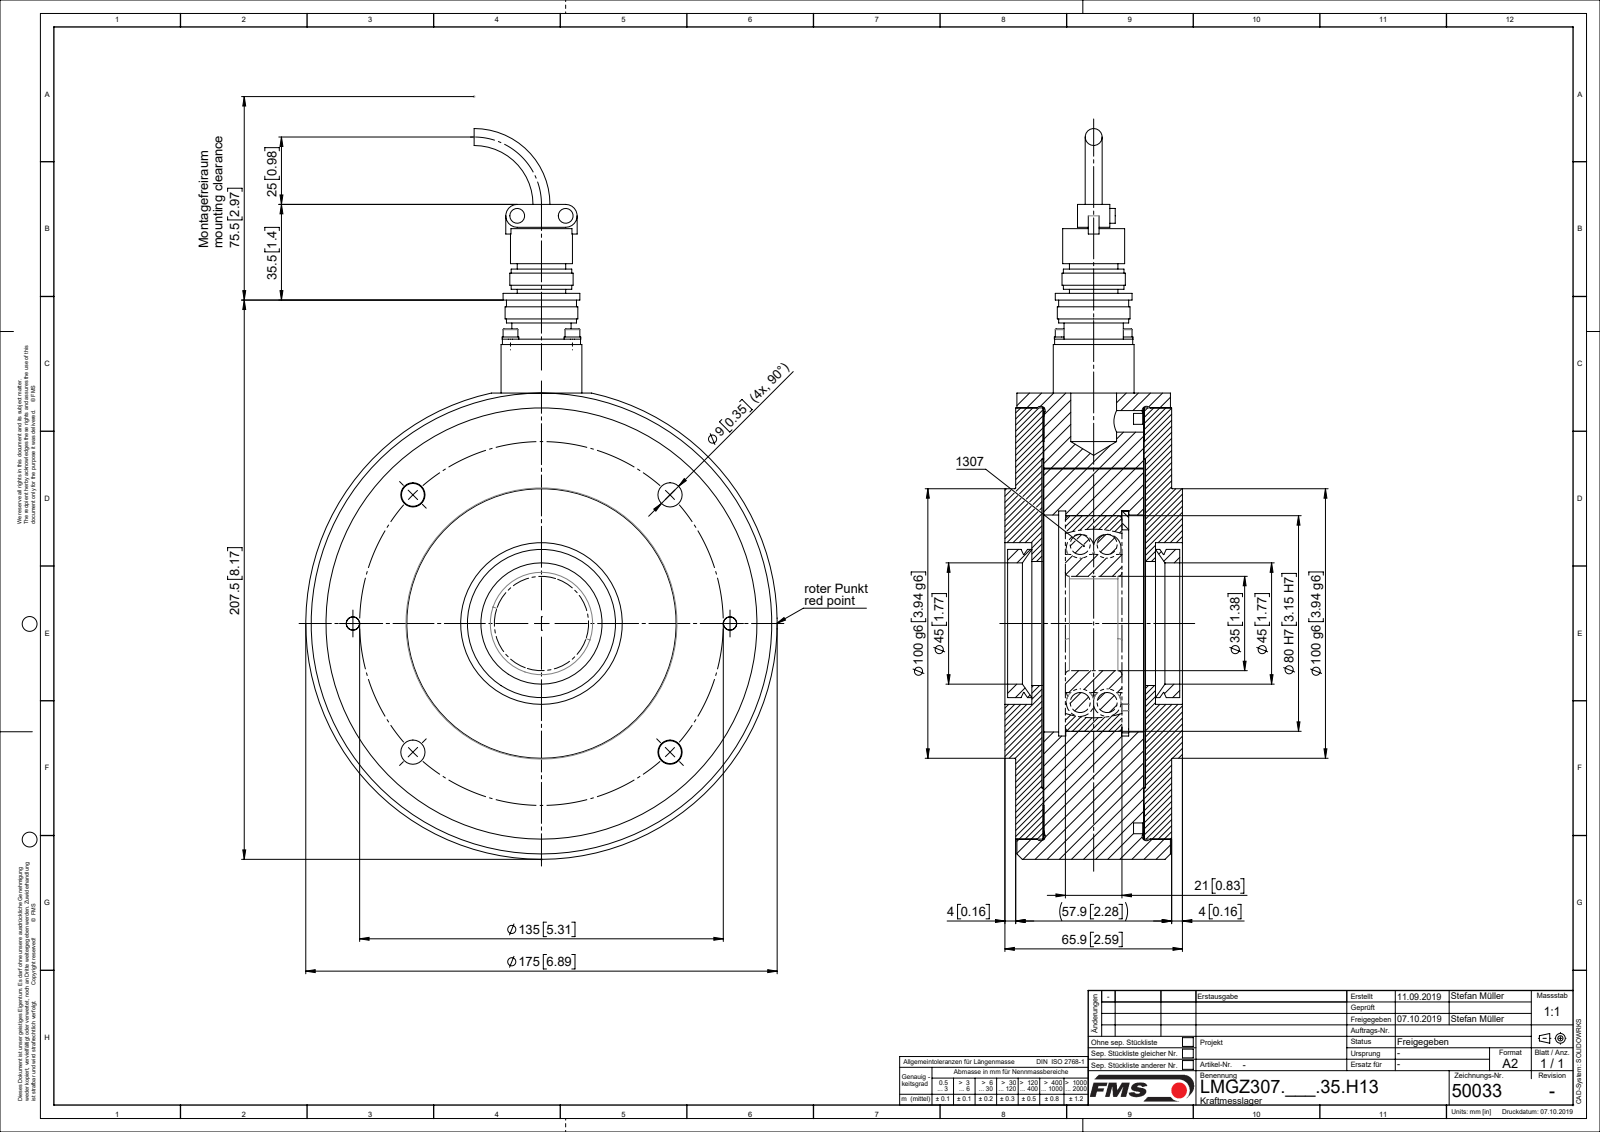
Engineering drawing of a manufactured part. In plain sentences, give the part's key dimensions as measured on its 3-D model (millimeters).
The part is named "L50033; L4857104; TEIL1; L48573 (+8 more)". Its 3-D file was written by "Mechanical Desktop 2007 (CONFIG_CONTROL_DESIGN)". It is 23 solids with 413 faces: 104 planar, 243 cylindrical and 66 other. Overall it measures 317.5 by 271.15 by 104.7 millimeters. Its volume is 1 290 000 cubic millimeters and its surface area 272 562 square millimeters. Round holes: 4 of diameter 2.6, 4 of diameter 3.2, 4 of diameter 3.4, 4 of diameter 9, 2 of diameter 5, 2 of diameter 6.6, 2 of diameter 11, 1 of diameter 8, 1 of diameter 10, 1 of diameter 23, 1 of diameter 35, 1 of diameter 44. Round bosses or shafts: 6 of diameter 5.5, 4 of diameter 6.2, 4 of diameter 3, 4 of diameter 2.5, 2 of diameter 10, 2 of diameter 6, 1 of diameter 175, 1 of diameter 160. Partial cylindrical surfaces (rounded edges, fillets, slot ends): 2 of radius 4.25, 2 of radius 7.5. The main face-to-face distances are 37.25, 10.2, 10.45, 47.45, 47.7, 37, 0.5, 38, 9.7, 48.2. The hole center spacings are 16.26, 23, 48.72, 52.67, 67.5, 95.46, 115.55, 127.04.
